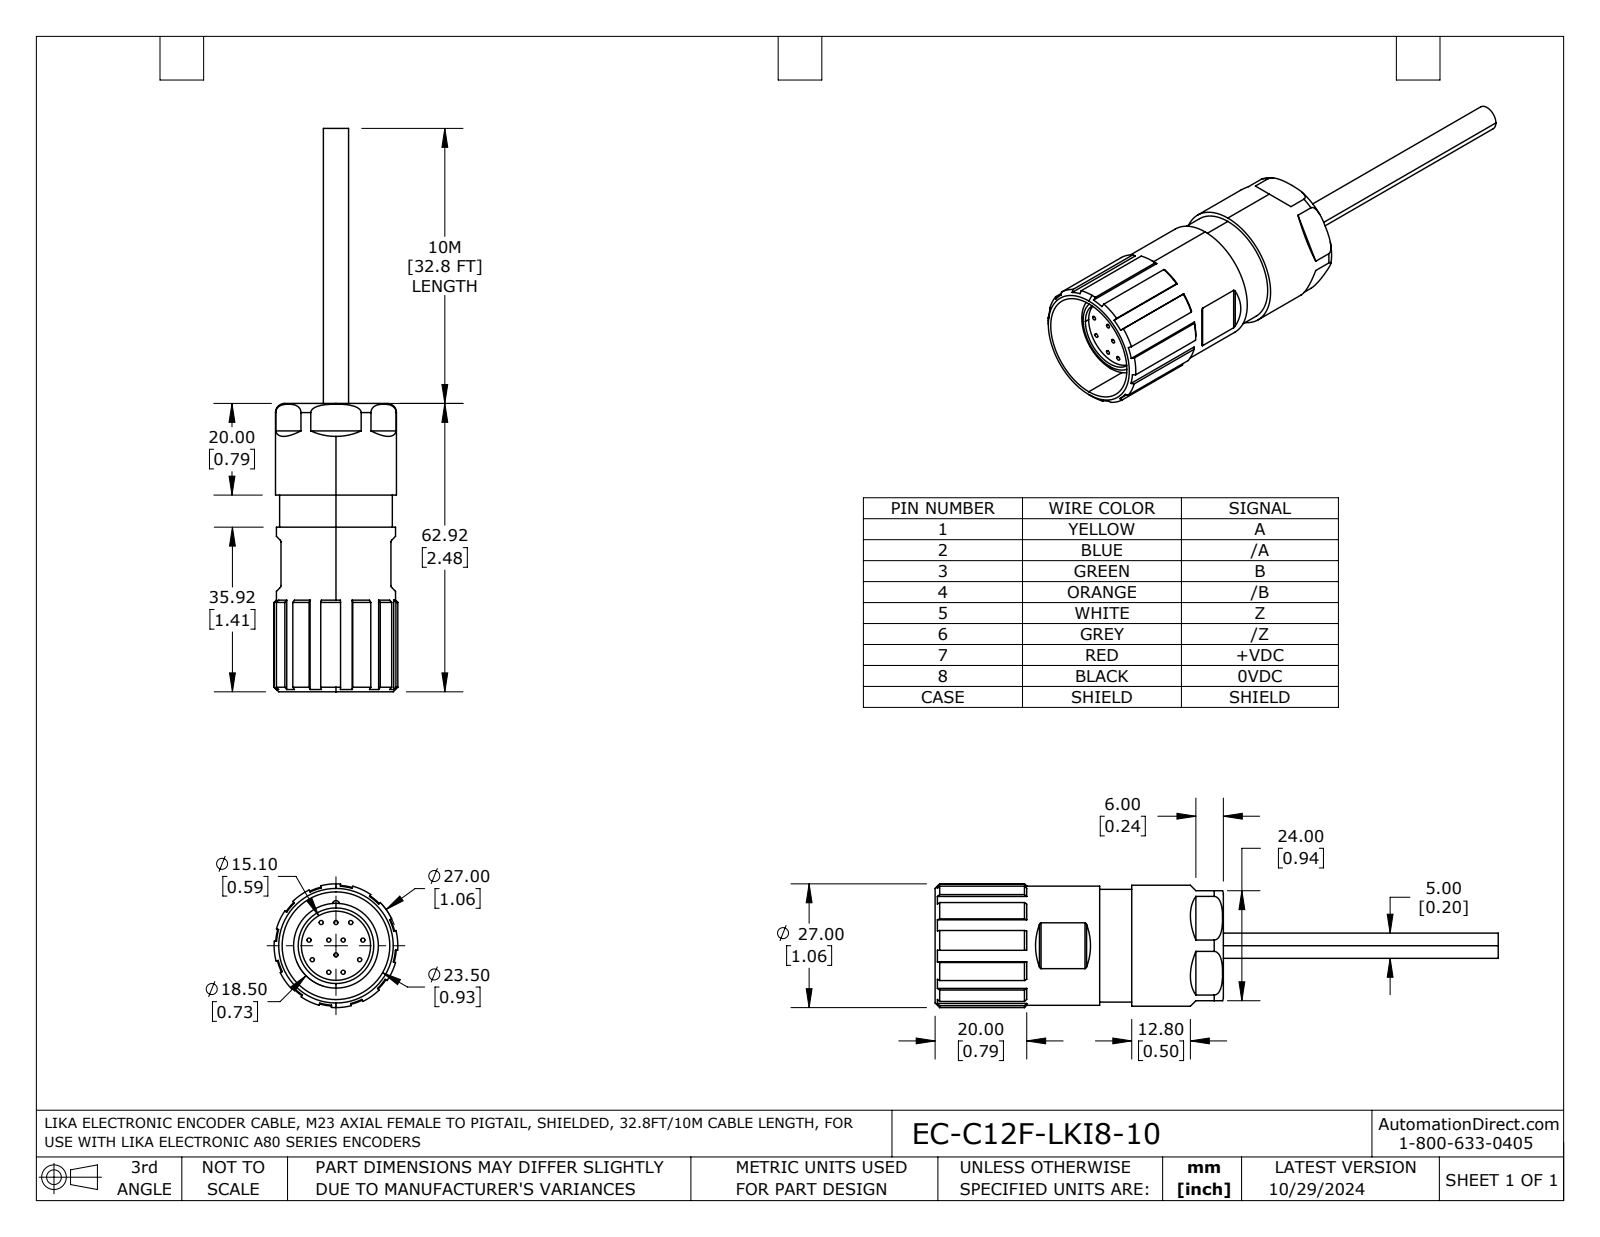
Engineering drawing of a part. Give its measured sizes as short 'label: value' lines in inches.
name: EC-C12F-LKI8-10
written by: SolidWorks 2021 (AUTOMOTIVE_DESIGN)
unit: in
bodies: 1 solid, 146 faces (64 planar, 63 cylindrical, 19 other)
size: 4.839 × 1.063 × 1.063
volume: 1.77 in³; area: 15.74 in²
holes: 12× ⌀0.035, 1× ⌀0.594, 1× ⌀0.677, 1× ⌀0.925
bosses: 1× ⌀1.039, 1× ⌀1.024, 1× ⌀0.969, 1× ⌀0.728, 1× ⌀0.217
rounds: 4× R0.02, 1× R0.03, 1× R0.531
face distances: 0.945, 1.985, 0.335, 1.65, 2.182, 1.847, 0.197, 0.591, 1.394, 1.06
hole spacings: 0.236, 0.079, 0.124, 0.127, 0.142, 0.162, 0.163, 0.164
